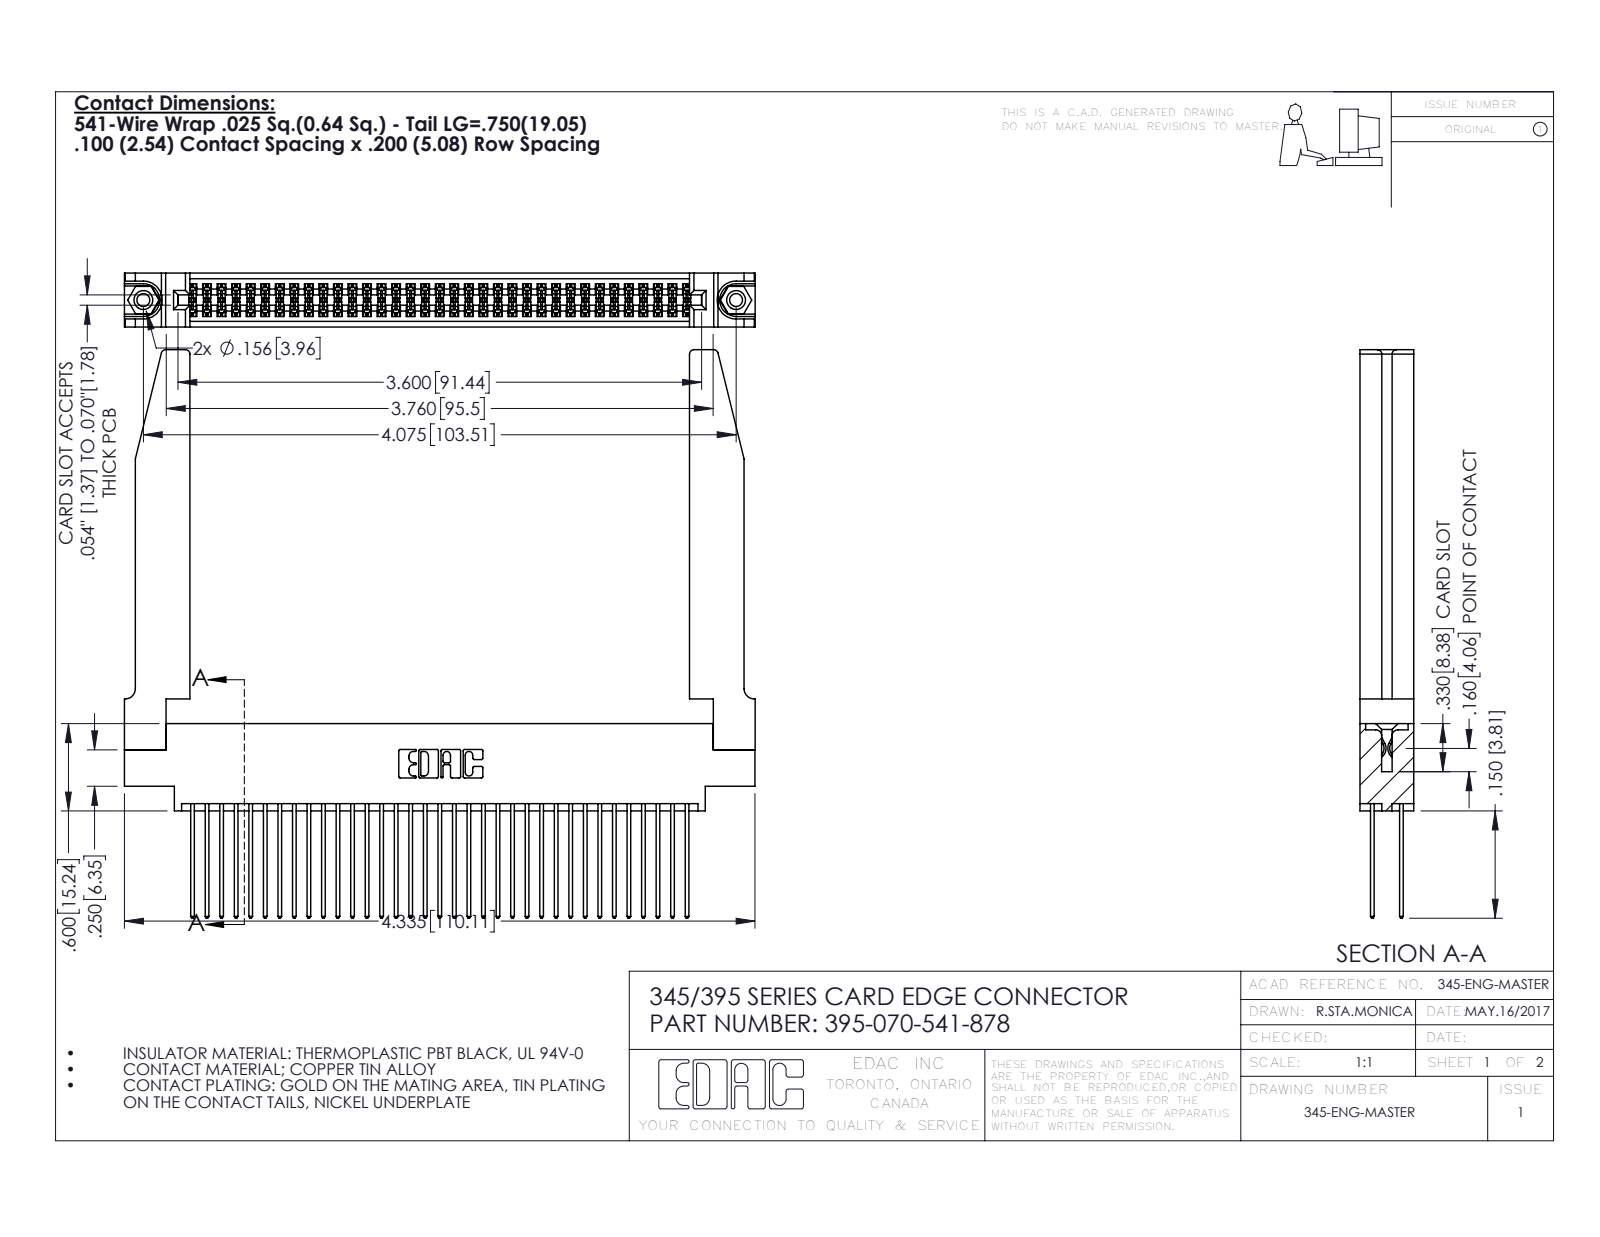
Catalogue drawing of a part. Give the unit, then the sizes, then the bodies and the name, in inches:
Units: inches
Overall size (bounding box): 4.336 × 3.907 × 0.37
Round holes (diameter × count): ⌀0.089 ×2, ⌀0.125 ×2, ⌀0.156 ×2, ⌀0.064 ×1
Round bosses / shafts (diameter × count): ⌀0.155 ×2
Partial cylindrical surfaces — rounded edges, fillets, slot ends (radius × count): R0.006 ×105, R0.01 ×70, R0.01 ×22, R0.03 ×8, R0.007 ×6, R0.031 ×6, R0.026 ×3, R0.014 ×2
Main face-to-face distances: 0.072, 0.298, 0.37, 0.098, 0.272, 0.025, 0.2, 0.225, 0.175, 0.148
Hole centre spacings: 0.27, 3.839, 4.075
Volume: 1.141 in³ · Surface area: 38.56 in²
Bodies: 75 solids, 3864 faces (2536 planar, 1276 cylindrical, 52 other)
Part name (STEP PRODUCT): 345-292-001_345-293-141; 345-250-001_345-250-001-102; 345 Part_0.170 Offset - 0.156 Dia-TH; 345-220-078_345-220-078 (+1 more)
STEP written by: SolidWorks 2016 (CONFIG_CONTROL_DESIGN)
